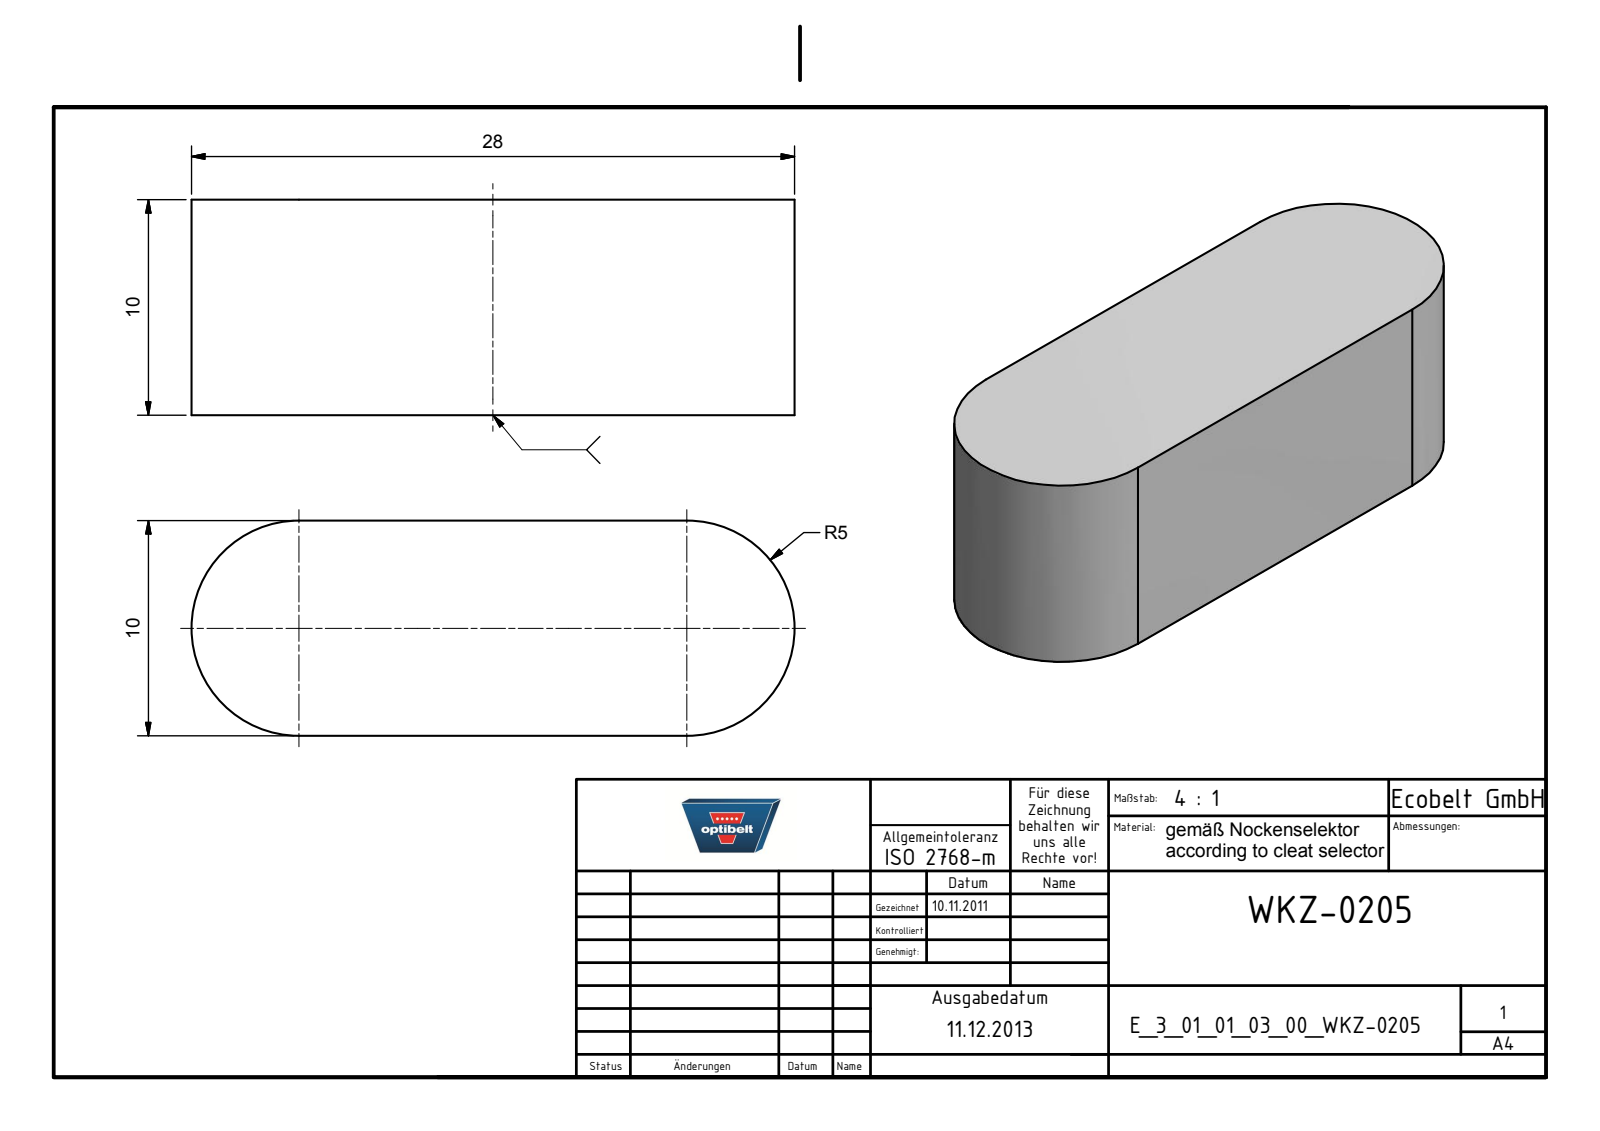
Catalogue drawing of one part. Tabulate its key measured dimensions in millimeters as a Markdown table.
| quantity | value |
| --- | --- |
| part name | E_3_01_01_03_00_WKZ-0205 |
| STEP written by | Autodesk Inventor 2021 (AUTOMOTIVE_DESIGN) |
| units | millimeters |
| bodies | 1 solid, 6 faces (4 planar, 2 cylindrical, 0 other) |
| overall size | 28 × 10 × 10 |
| volume | 2 585 mm³ |
| surface area | 1 191 mm² |
| partial cylindrical surfaces (radius × count) | 5 × 2 |
| main face-to-face distances | 10 |
